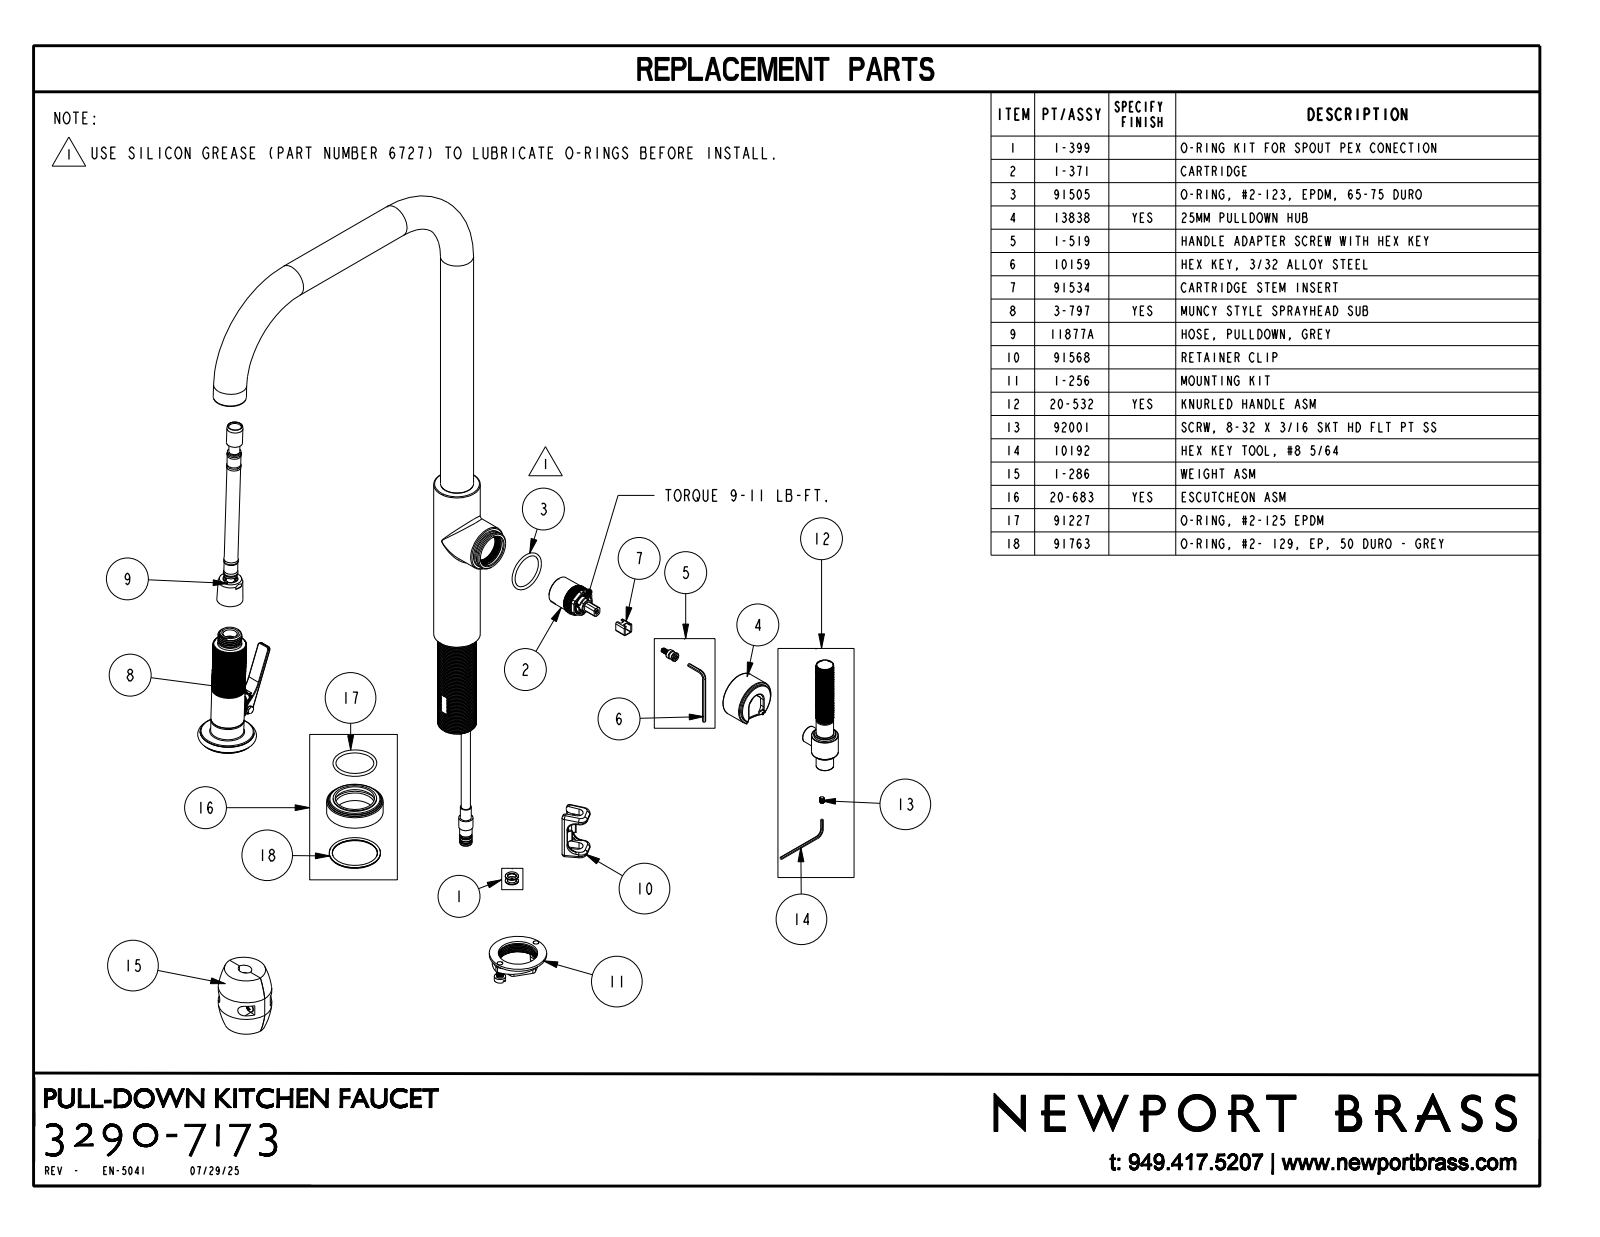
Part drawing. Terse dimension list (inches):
name: 3290-7173
written by: CREO PARAMETRIC BY PTC INC, 2025093 (CONFIG_CONTROL_DESIGN)
unit: in
bodies: 4 solids, 21004 faces (579 planar, 4013 cylindrical, 16412 other)
size: 19.995 × 13.158 × 4.347
volume: 48.59 in³; area: 179.2 in²
holes: 1× ⌀0.228, 1× ⌀1.035
bosses: 18× ⌀0.102, 2× ⌀1.14, 1× ⌀1.94, 1× ⌀1.855, 1× ⌀1.78, 1× ⌀1.6, 1× ⌀1.56, 1× ⌀1.4
rounds: 26× R0.02, 17× R0.03, 15× R0.06, 7× R0.025, 4× R0.045, 3× R0.1, 2× R0.065, 2× R0.2
face distances: 6.86, 0.308, 0.025, 3.959, 3.651, 6.88, 0.02, 3.933, 3.626, 0.099
